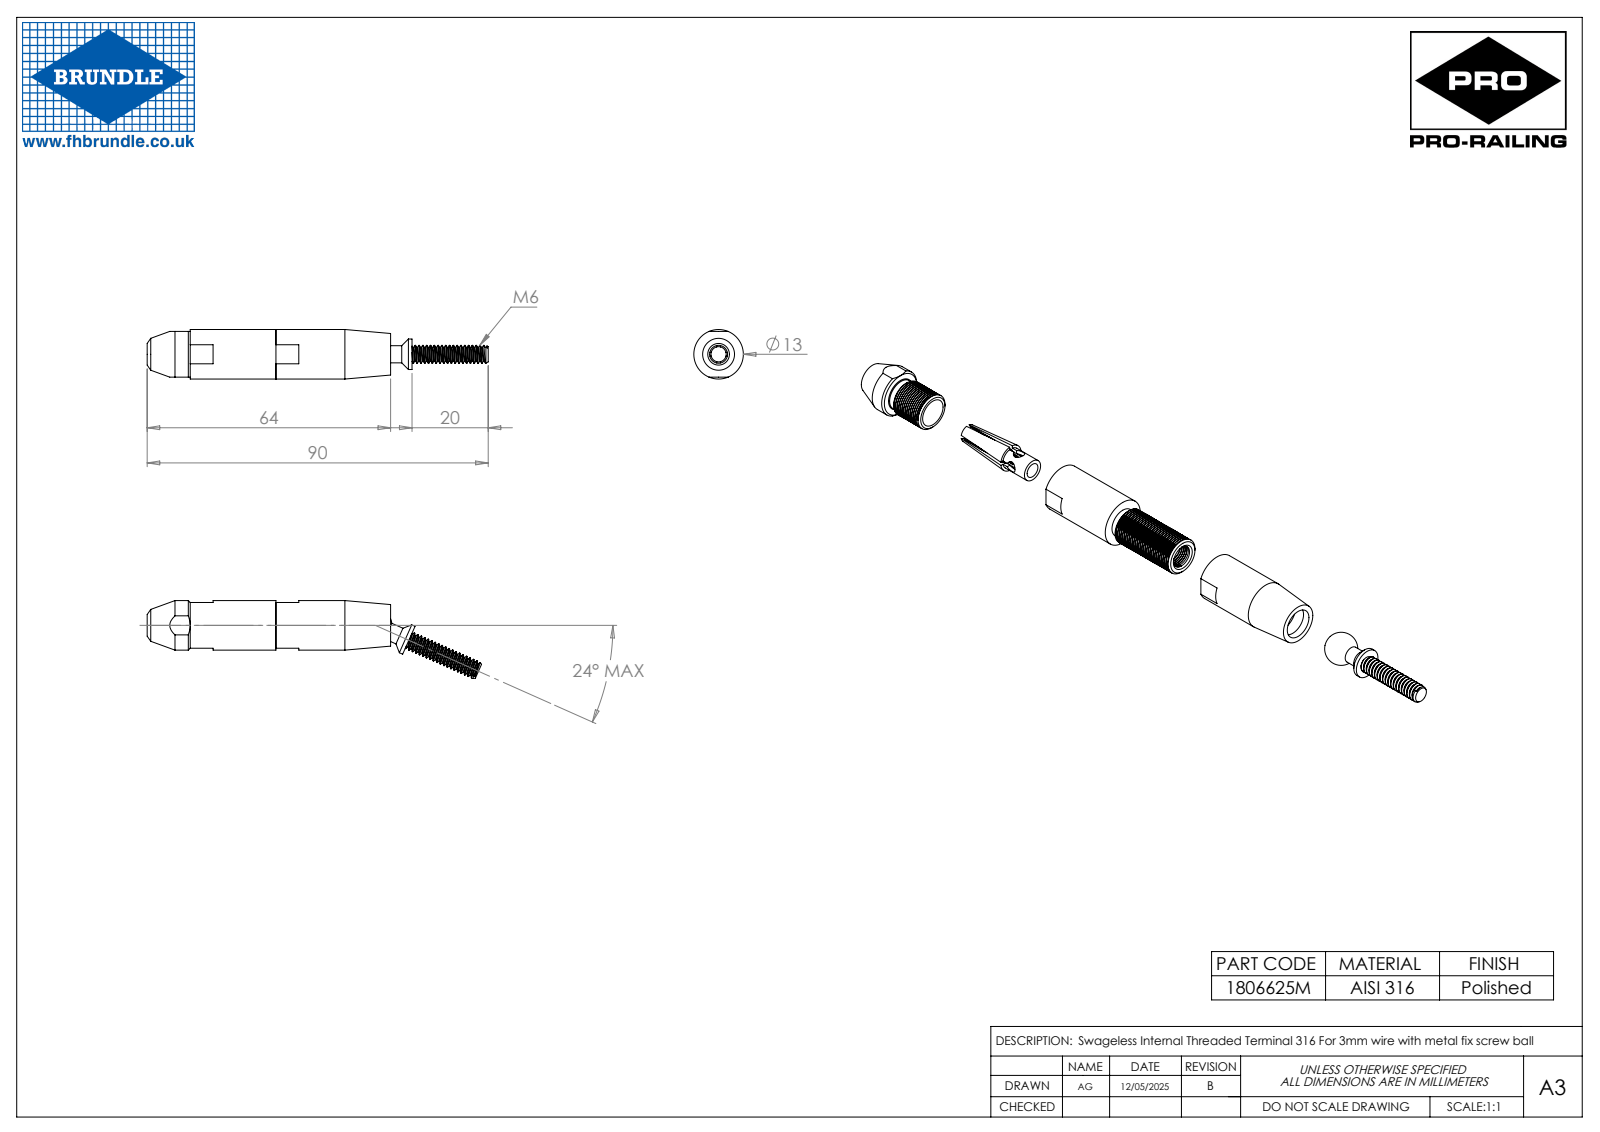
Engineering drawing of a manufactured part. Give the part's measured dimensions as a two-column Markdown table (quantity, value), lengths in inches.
| quantity | value |
| --- | --- |
| part name | 1806625; 1806625 part2_with thread; 1806625 part1_with thread; 1806625M (+3 more) |
| STEP written by | SolidWorks 2023 (CONFIG_CONTROL_DESIGN) |
| units | inches |
| bodies | 5 solids, 857 faces (60 planar, 471 cylindrical, 326 other) |
| overall size | 3.524 × 0.512 × 0.512 |
| volume | 0.349 in³ |
| surface area | 15.31 in² |
| round holes (diameter × count) | 0.118 × 2, 0.157 × 1, 0.236 × 1, 0.317 × 1, 0.394 × 1 |
| round bosses / shafts (diameter × count) | 0.512 × 1, 0.335 × 1, 0.315 × 1, 0.185 × 1, 0.177 × 1 |
| main face-to-face distances | 0.217, 0.256, 0.472, 0.886, 0.039, 0.079, 1.106, 0.138, 0.748, 1.185 |
